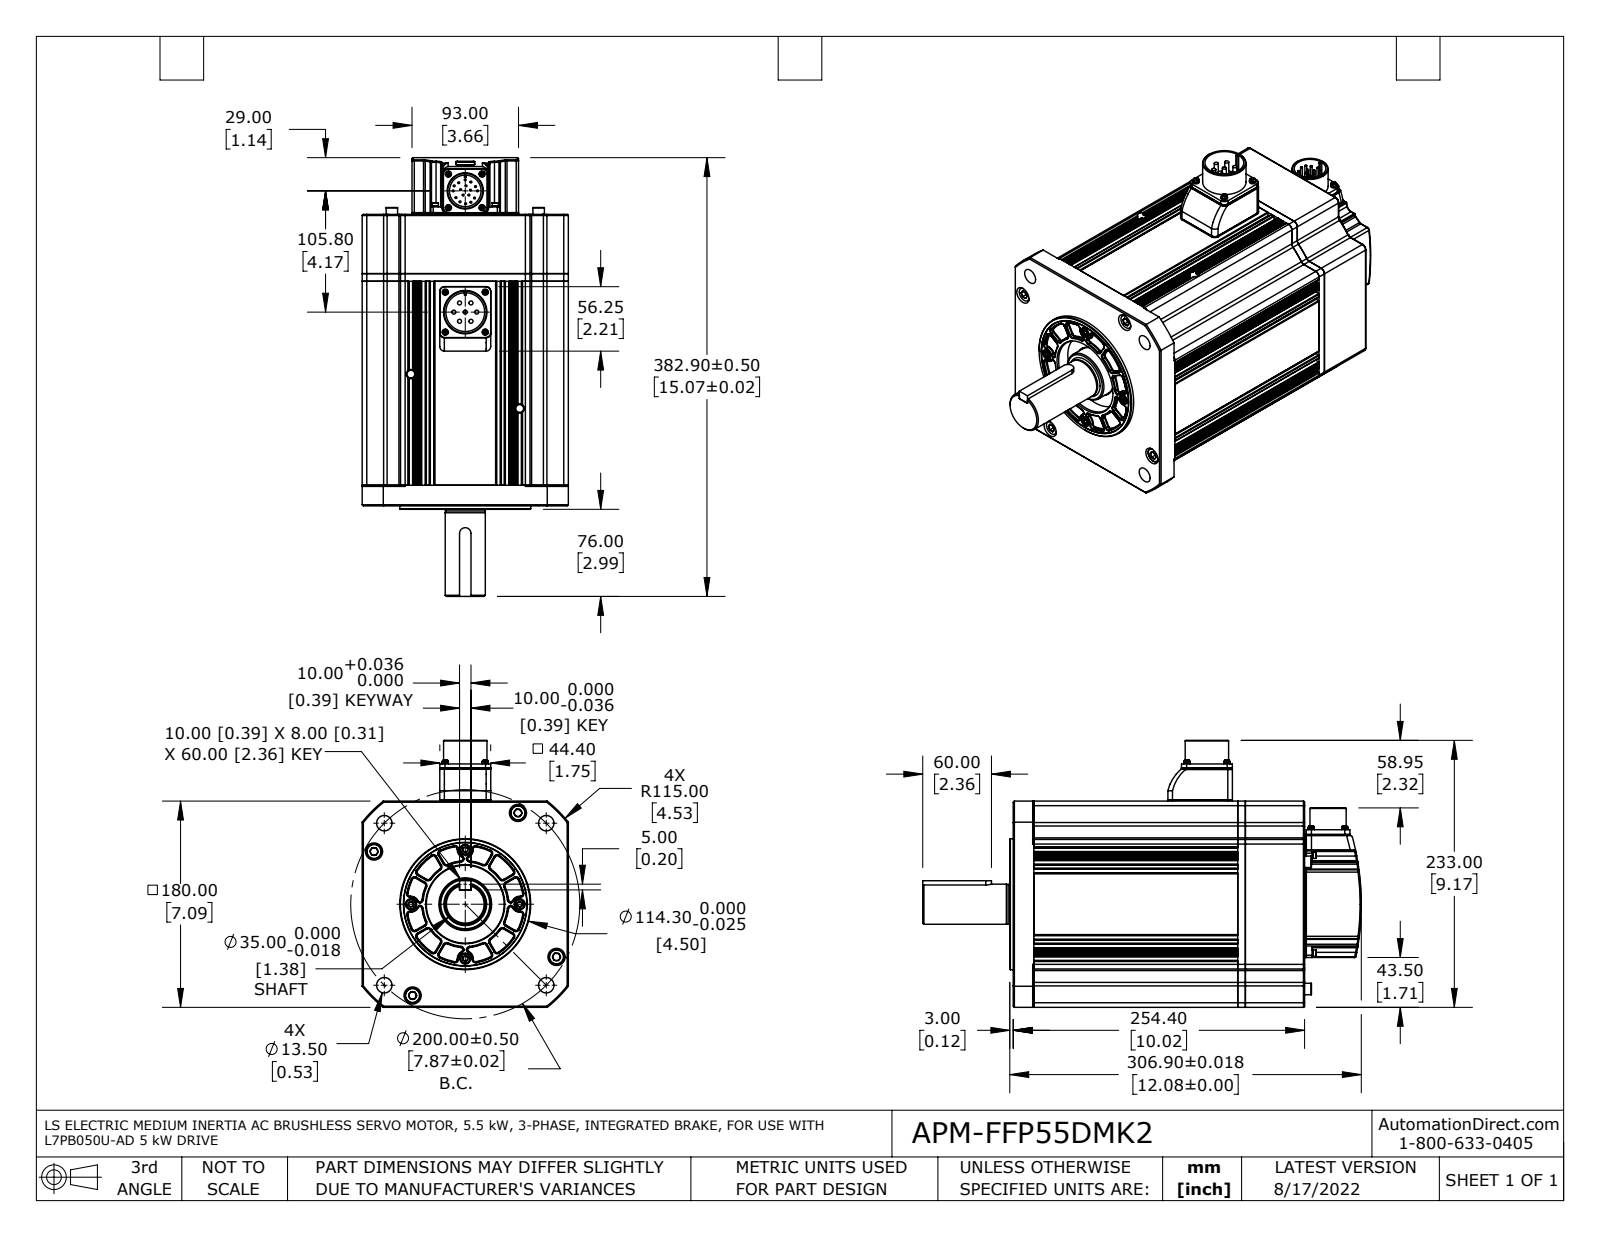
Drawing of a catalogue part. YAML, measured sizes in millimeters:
part_name: "FMP18GA003G03_Out Line(APM-FFP55D_K2) r1 nc fxt"
step_written_by: "SolidWorks 2017 (AUTOMOTIVE_DESIGN)"
units: millimeters
bodies: {solids: 64, faces: 2543, planar: 834, cylindrical: 965, other: 744}
overall_size: [382.9, 233, 180]
volume: 7672000
surface_area: 625400
round_holes:
  - {diameter: 3, count: 17}
  - {diameter: 2.5, count: 9}
  - {diameter: 6, count: 8}
  - {diameter: 6.8, count: 8}
  - {diameter: 9.5, count: 8}
  - {diameter: 3, count: 4}
  - {diameter: 3.5, count: 4}
  - {diameter: 3.6, count: 4}
  - {diameter: 3.7, count: 4}
  - {diameter: 3.7, count: 4}
  - {diameter: 5, count: 4}
  - {diameter: 8, count: 4}
round_bosses_or_shafts:
  - {diameter: 1.6, count: 17}
  - {diameter: 5.4, count: 8}
  - {diameter: 3.5, count: 7}
  - {diameter: 13.2, count: 4}
  - {diameter: 13, count: 4}
  - {diameter: 8.5, count: 4}
  - {diameter: 8, count: 4}
  - {diameter: 5.5, count: 4}
partial_cylinders:
  - {radius: 0.5, count: 124}
  - {radius: 2.5, count: 56}
  - {radius: 4, count: 24}
  - {radius: 1, count: 22}
  - {radius: 2, count: 17}
  - {radius: 4.5, count: 12}
  - {radius: 6.5, count: 4}
  - {radius: 0.3, count: 2}
face_to_face_distances: [6.7, 184.7, 178, 180, 1, 18, 33.5, 146.5, 10, 8]
hole_center_spacings: [32.6, 33.4, 34.1, 74.4, 92, 137.7, 26.3, 56.1]
